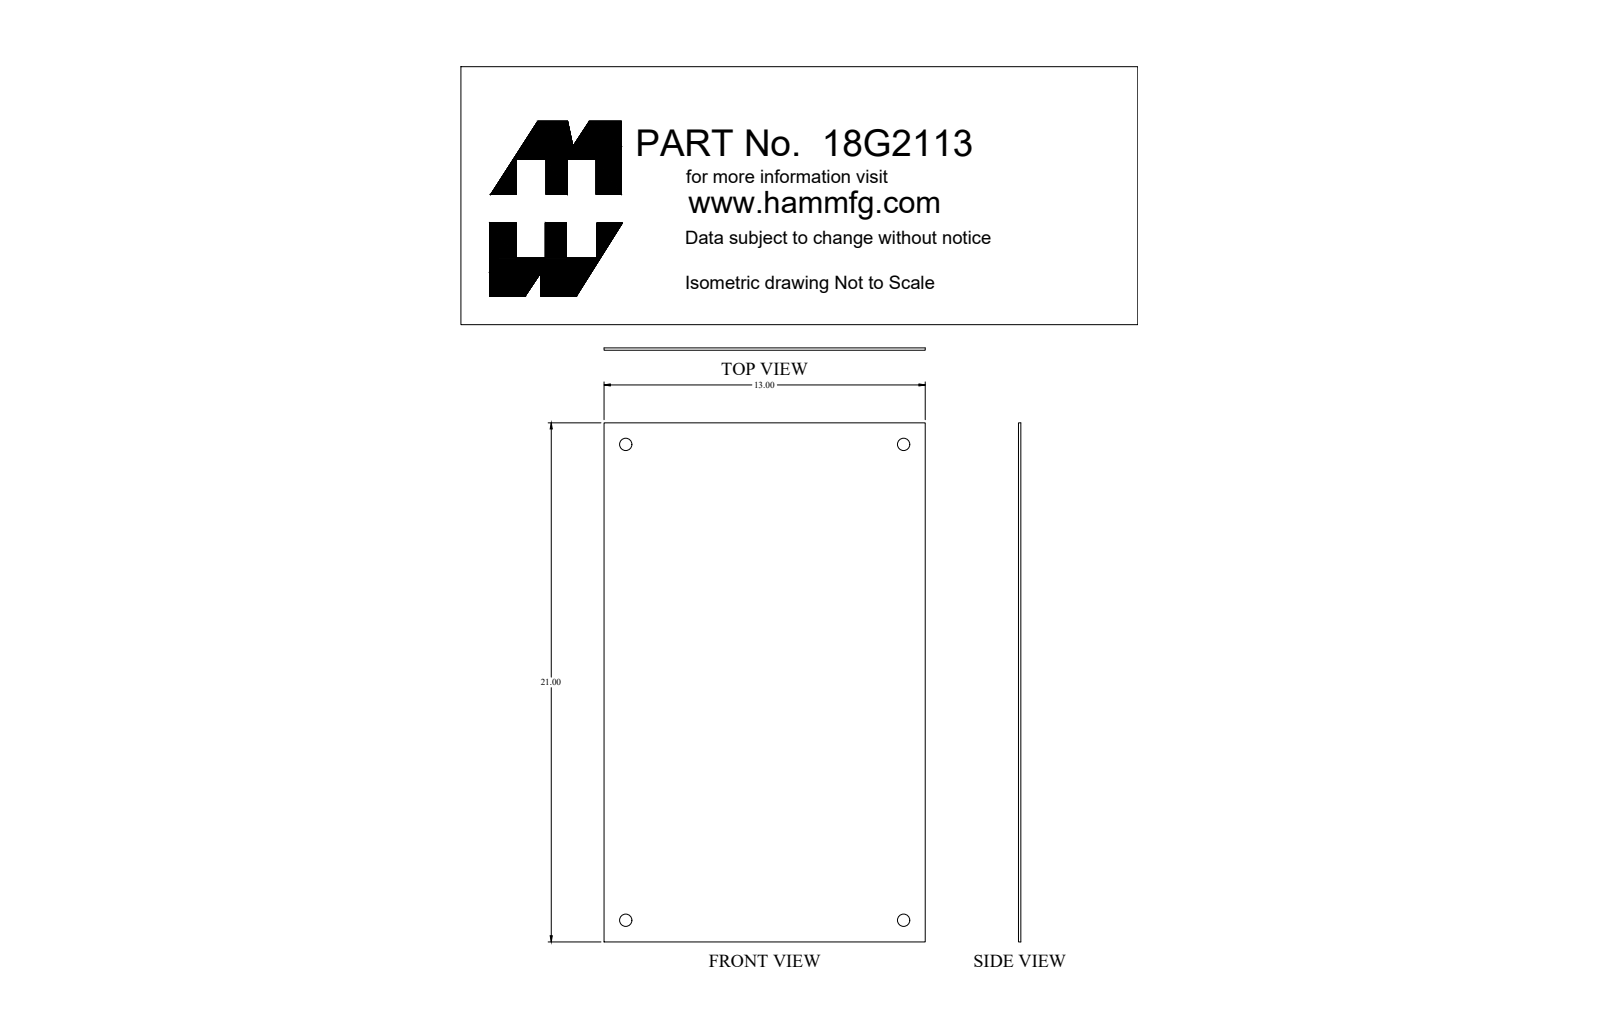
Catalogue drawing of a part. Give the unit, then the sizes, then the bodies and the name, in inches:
Units: inches
Overall size (bounding box): 21 × 13 × 0.095
Round holes (diameter × count): ⌀0.5 ×4
Main face-to-face distances: 0.095, 13, 21
Hole centre spacings: 11.25, 19.25, 22.296
Volume: 25.86 in³ · Surface area: 551.5 in²
Bodies: 1 solid, 10 faces (6 planar, 4 cylindrical, 0 other)
Part name (STEP PRODUCT): 18G2113
STEP written by: SolidWorks 2018 (AUTOMOTIVE_DESIGN)
